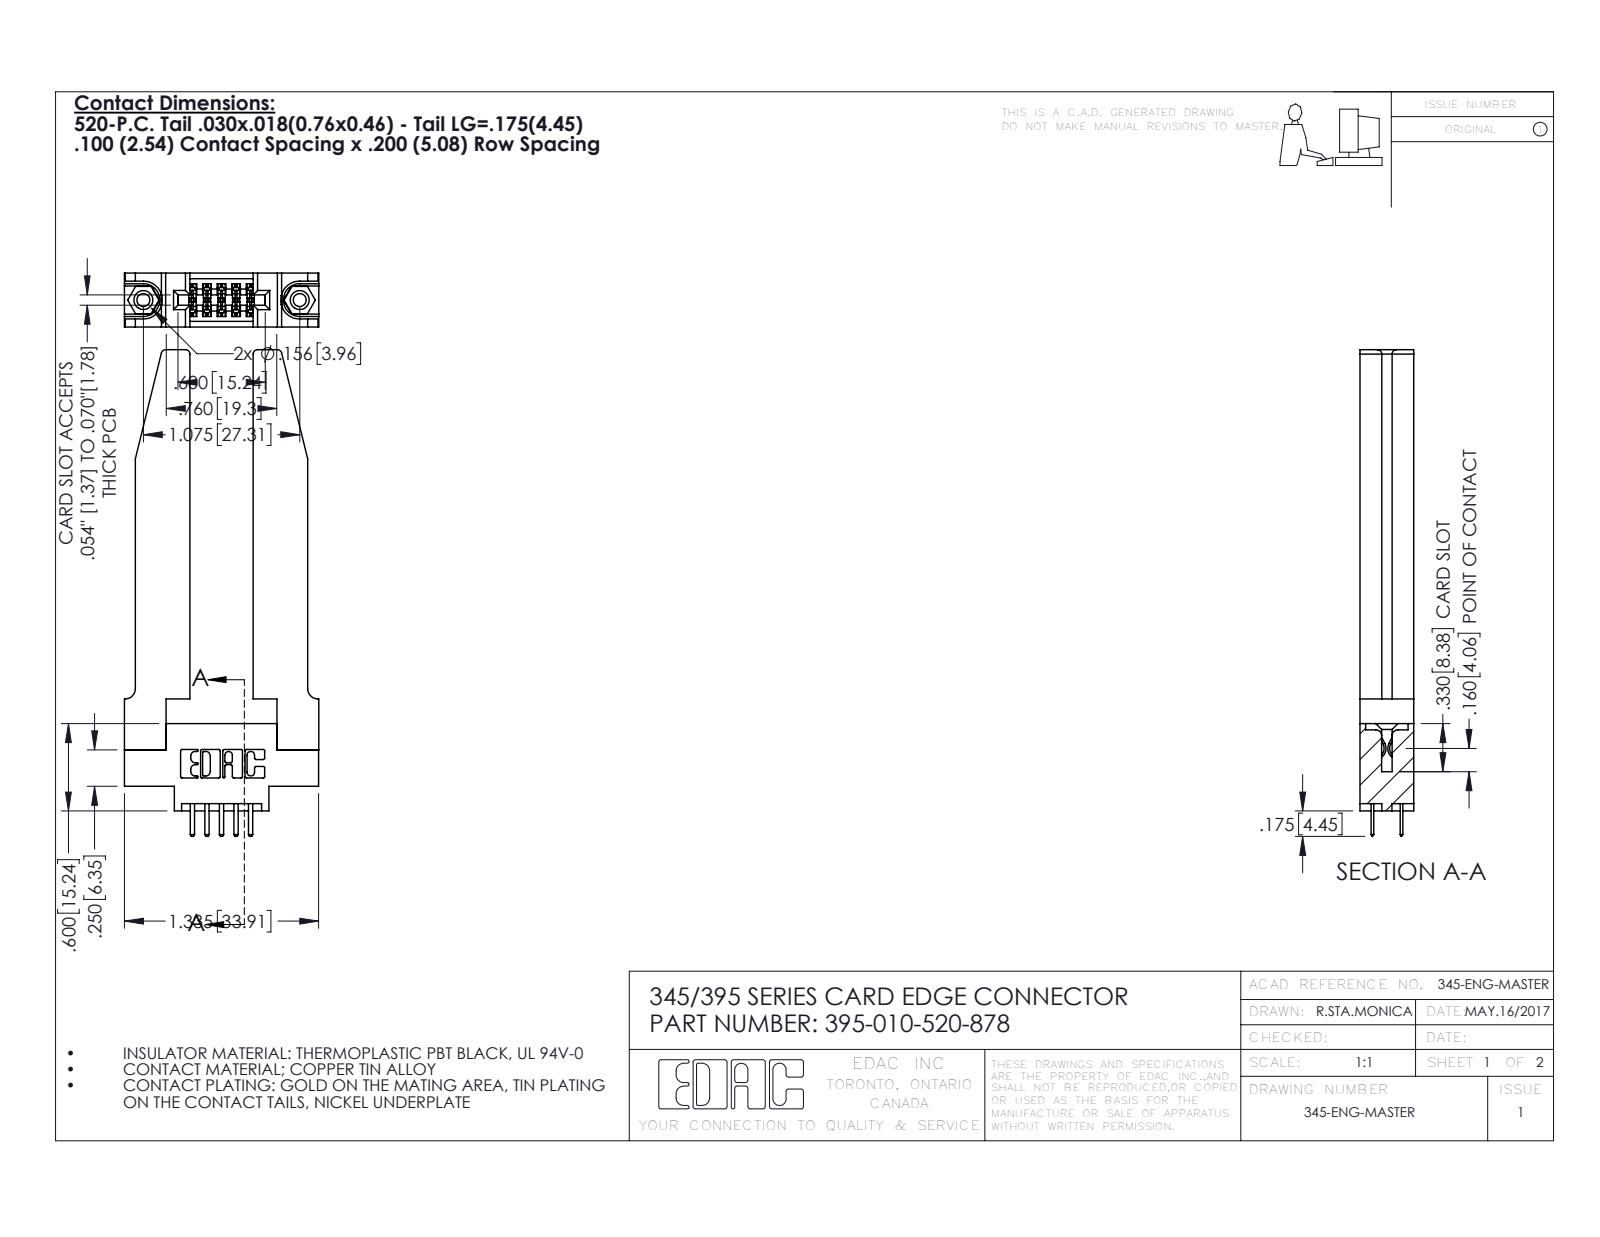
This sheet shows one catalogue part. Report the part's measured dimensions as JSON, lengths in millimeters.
{"part_name": "345-220-078_345-220-078; 395-010-520-878; 345-250-001_345-250-001-102; 345 Part_0.170 Offset - 0.156 Dia-TH (+1 more)", "step_written_by": "SolidWorks 2016 (CONFIG_CONTROL_DESIGN)", "units": "millimeters", "bodies": {"solids": 15, "faces": 904, "planar": 576, "cylindrical": 276, "other": 52}, "overall_size": [85, 33.9, 9.4], "volume_mm3": 10600, "surface_area_mm2": 10450, "round_holes": [[2.3, 2], [3.2, 2], [4, 2], [1.6, 1]], "round_bosses_or_shafts": [[3.9, 2]], "partial_cylinders_radius": [[0.3, 22], [0.2, 15], [0.3, 14], [0.8, 8], [0.2, 6], [0.8, 6], [0.7, 3], [0.4, 2]], "face_to_face_distances": [9.4, 3.8, 5.6, 11, 1.8, 7.6, 2, 3.8, 2.4, 1.4], "hole_center_spacings": [6.9, 21.5, 27.3]}
